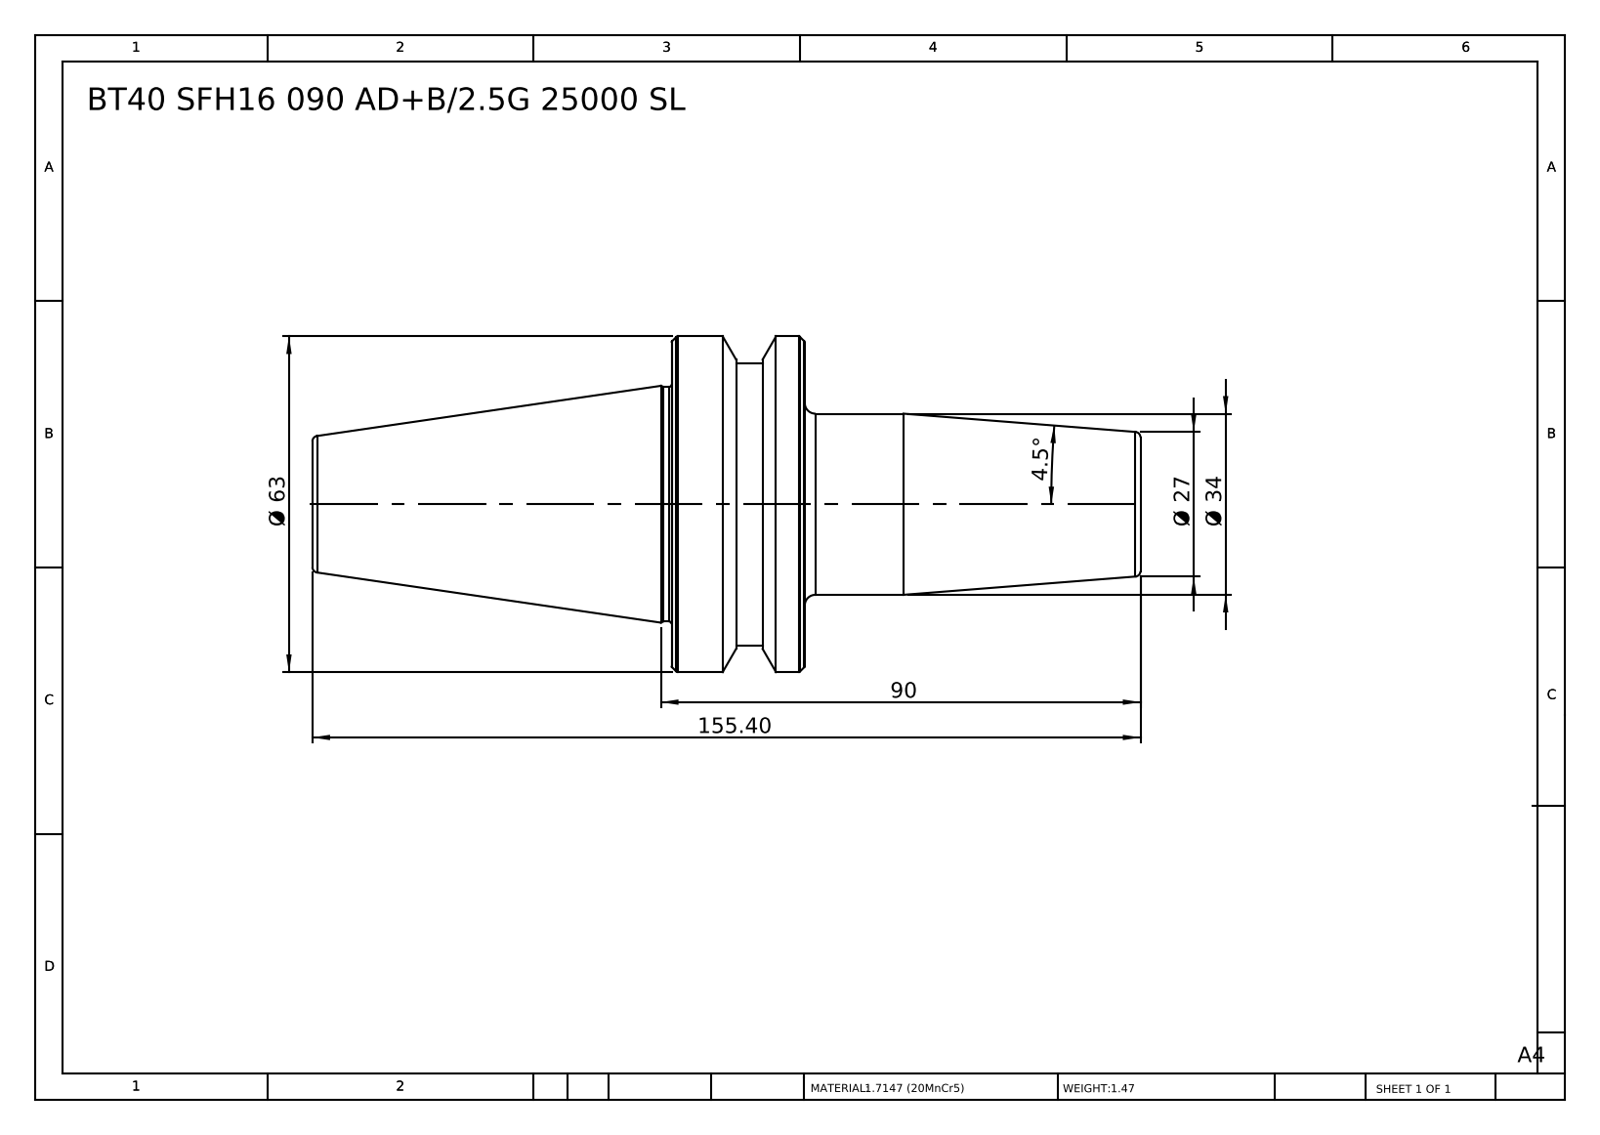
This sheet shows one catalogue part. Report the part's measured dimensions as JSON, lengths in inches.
{"part_name": "BT40 SFH14 090 AD+B-2.5G 25000 SL", "step_written_by": "SolidWorks 2014 (CONFIG_CONTROL_DESIGN)", "units": "inches", "bodies": {"solids": 1, "faces": 46, "planar": 6, "cylindrical": 10, "other": 30}, "overall_size": [6.118, 2.48, 2.48], "volume_in3": 11.47, "surface_area_in2": 37.38, "round_bosses_or_shafts": [[2.48, 1], [2.087, 1], [1.732, 1], [1.339, 1]], "face_to_face_distances": [0.984, 2.48, 3.465, 6.118, 3.638, 2.654, 2.791, 0.311, 0.673, 3.327]}
